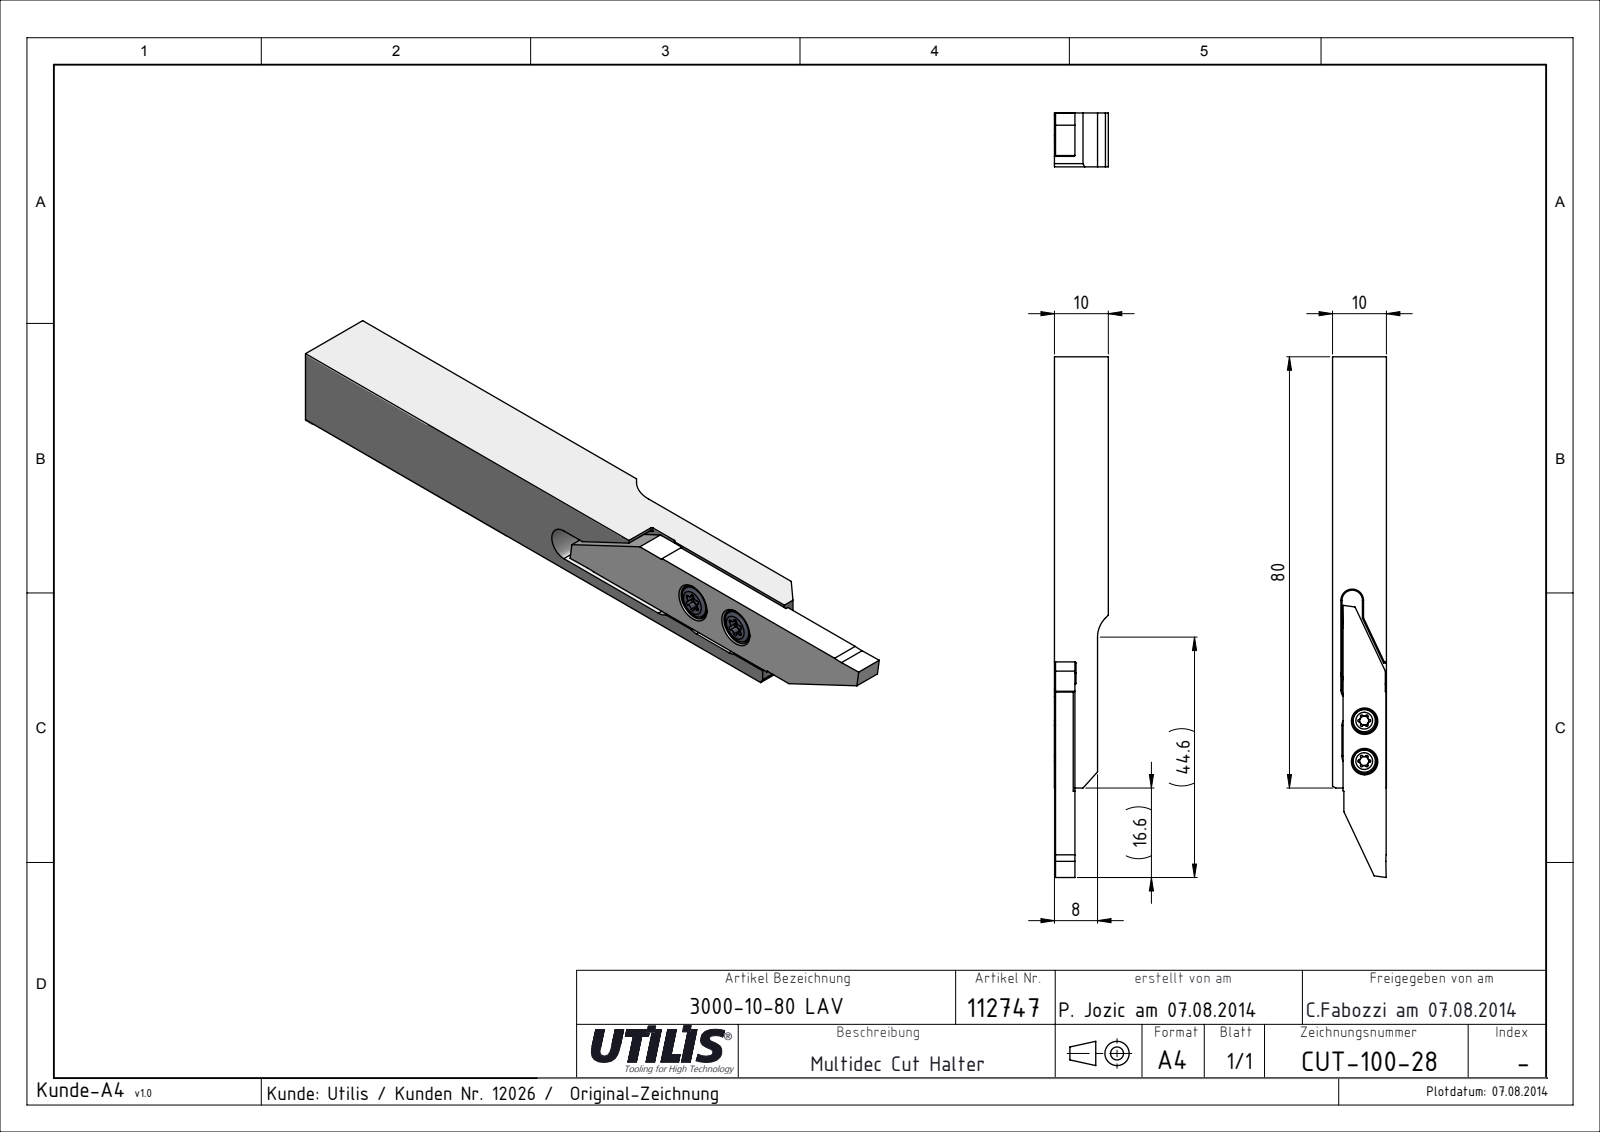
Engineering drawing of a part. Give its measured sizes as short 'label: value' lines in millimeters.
name: CUT-100-28
written by: SolidWorks 2016 (AUTOMOTIVE_DESIGN)
unit: mm
bodies: 1 solid, 45 faces (33 planar, 8 cylindrical, 4 other)
size: 96.6 × 10 × 10
volume: 7 532 mm³; area: 3 833 mm²
rounds: 4× R2.1, 2× R10, 1× R5
face distances: 10, 8, 9.8, 7.8, 2, 4.2, 3.8, 3.6, 6.2, 9.95
